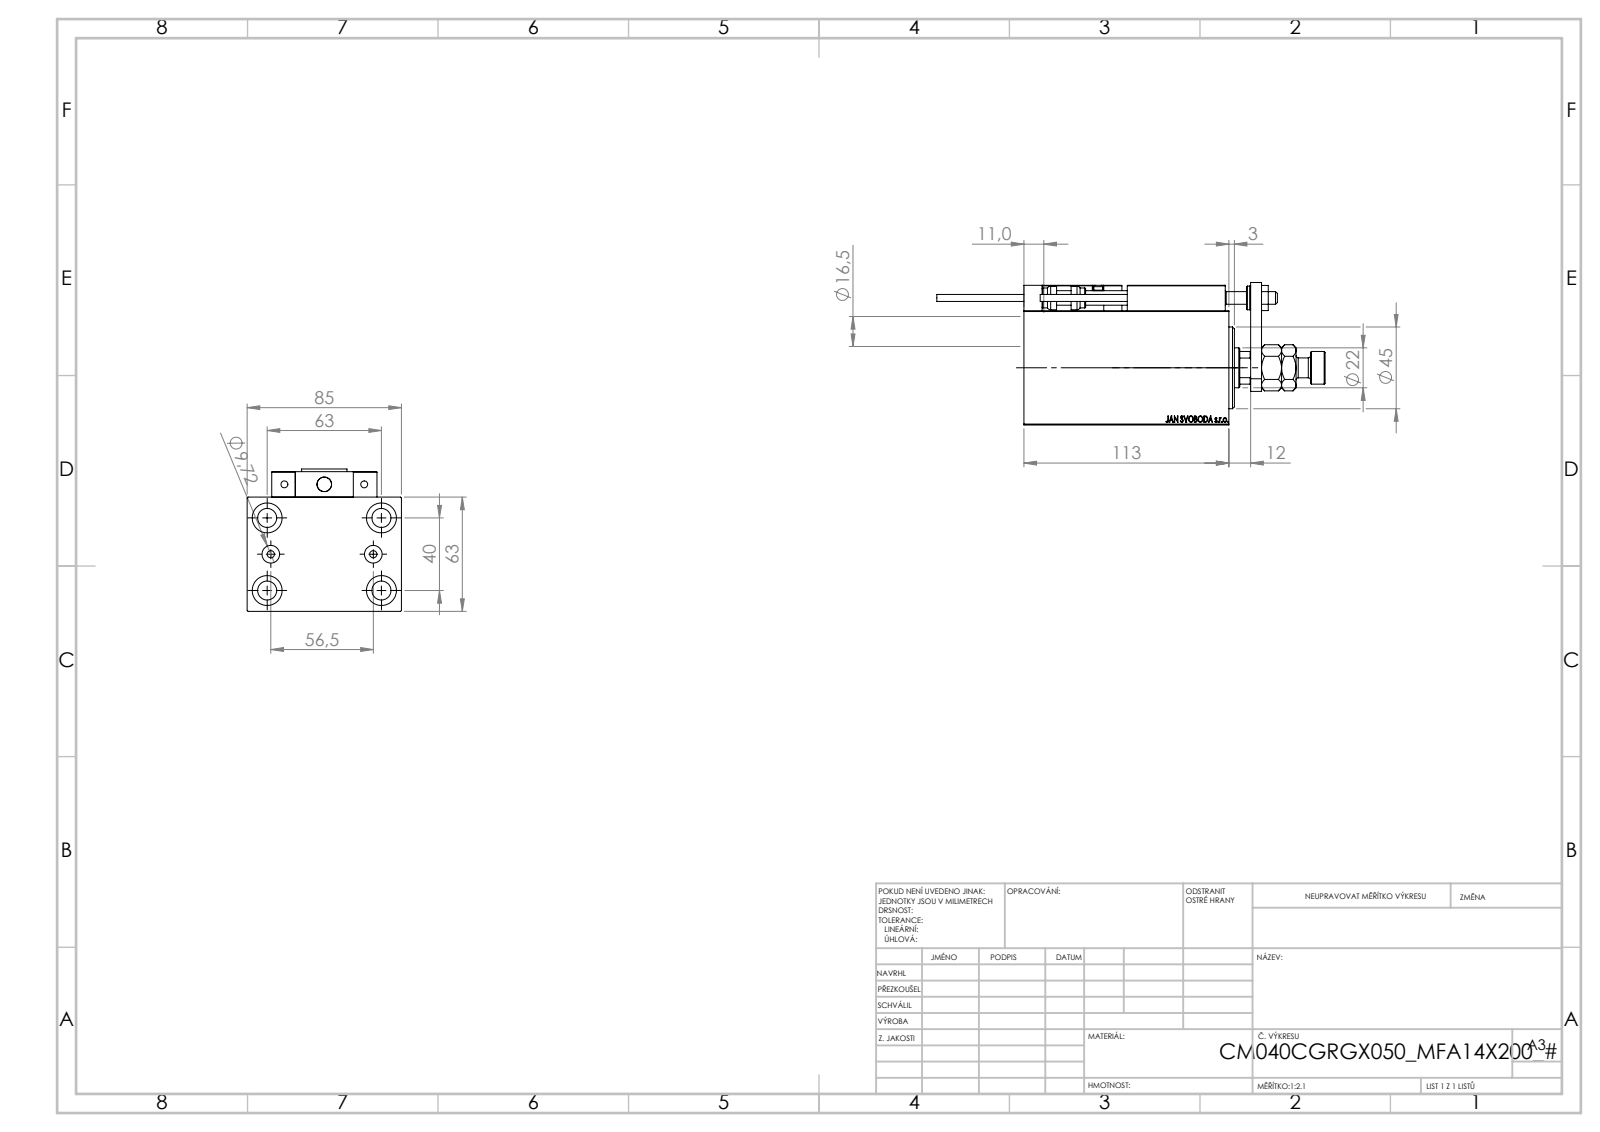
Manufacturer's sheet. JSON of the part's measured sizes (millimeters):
{"part_name": "ZARAZKA; ALLEN BOLT D8; KONCOVKA; SWITCH X (+7 more)", "step_written_by": "SolidWorks 2019 (CONFIG_CONTROL_DESIGN)", "units": "millimeters", "bodies": {"solids": 24, "faces": 1330, "planar": 576, "cylindrical": 188, "other": 566}, "overall_size": [214, 85, 78.5], "volume_mm3": 572473, "surface_area_mm2": 125555, "round_holes": [[4, 6], [8, 5], [16.5, 5], [3.2, 4], [10.5, 4], [5, 2], [9.72, 2], [7, 1], [12.5, 1], [22, 1], [25.5, 1], [40, 1]], "round_bosses_or_shafts": [[11, 2], [5, 2], [3.8, 2], [18, 1], [13, 1]], "partial_cylinders_radius": [[0.3, 30], [3, 2], [10.5, 1]], "face_to_face_distances": [63, 85, 12, 113, 101, 14, 18, 77, 20, 6], "hole_center_spacings": [20.26, 37.31, 63.01, 11.37, 20, 28.25, 29.59, 29.69]}
